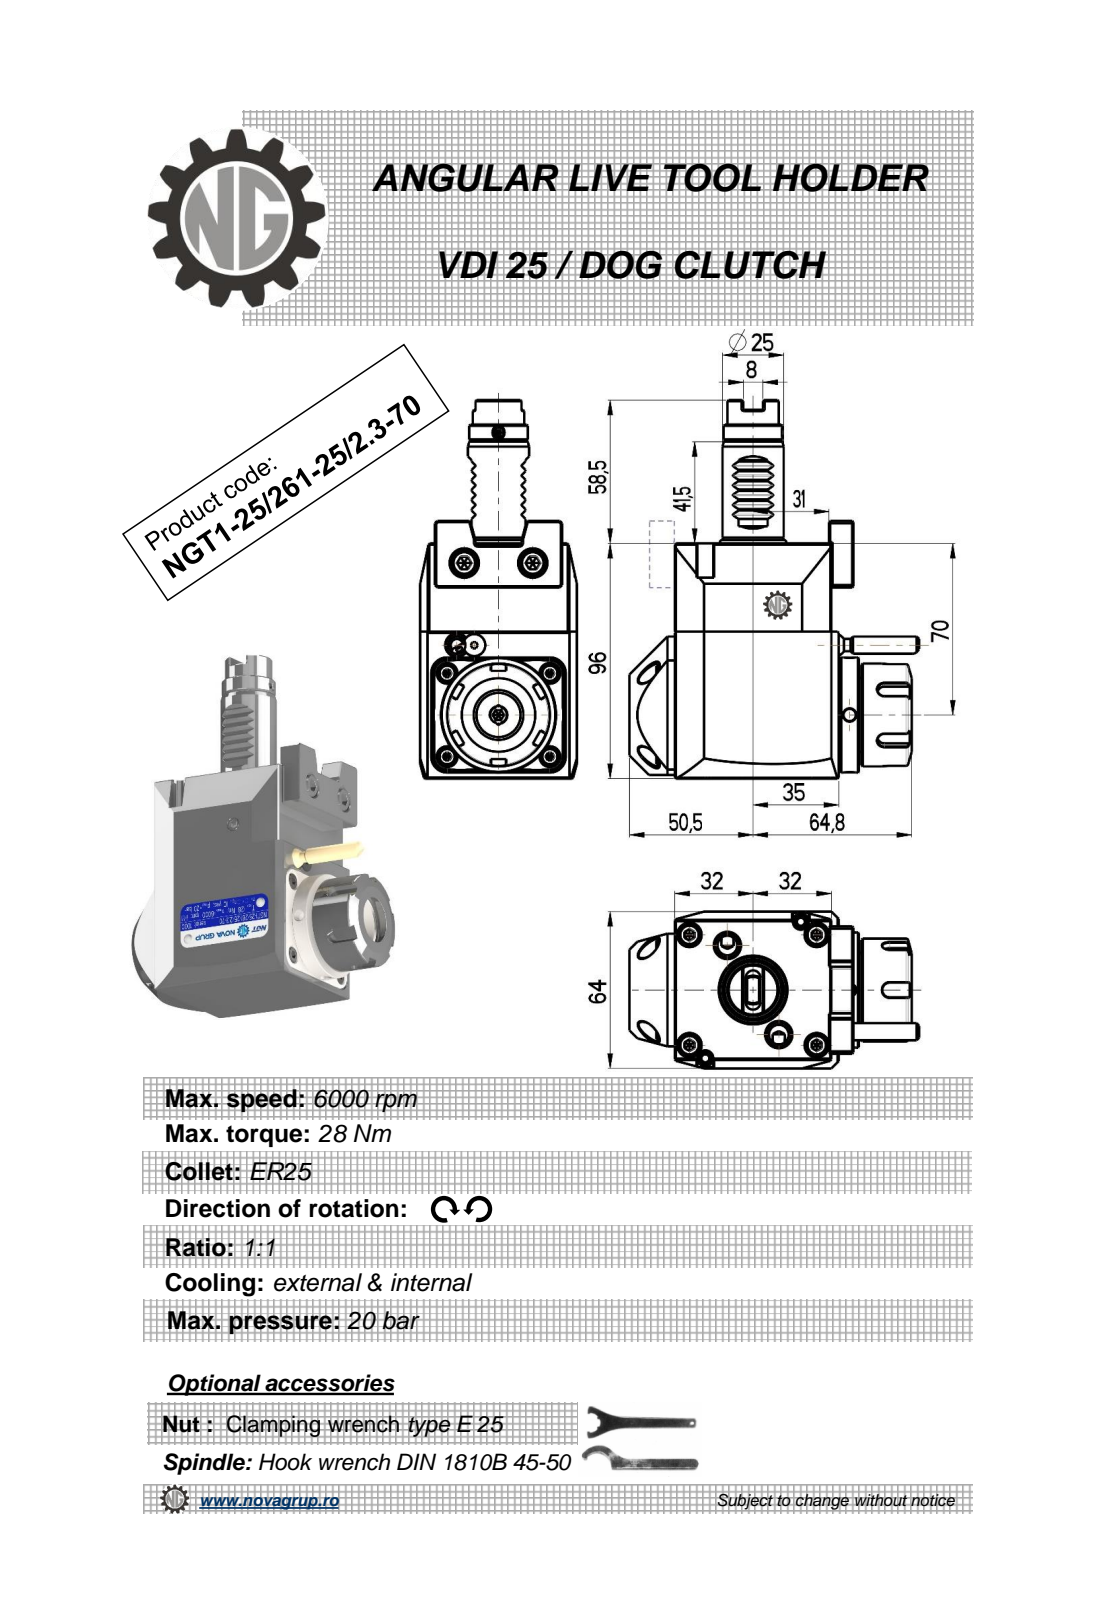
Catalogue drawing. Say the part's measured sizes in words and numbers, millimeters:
The part is named "NGT1_25_261_25_2_3_70". Its 3-D file was written by "PRO/ENGINEER BY PARAMETRIC TECHNOLOGY CORPORATION, 2010280 (CONFIG_CONTROL_DESIGN)". It is 1 solid with 418 faces: 214 planar, 66 cylindrical and 138 other. Overall it measures 154.5 by 118.33 by 64 millimeters. Its volume is 505 431 cubic millimeters and its surface area 49 640 square millimeters. Round holes: 2 of diameter 5, 1 of diameter 2.5, 1 of diameter 3, 1 of diameter 20.3. Round bosses or shafts: 1 of diameter 47, 1 of diameter 42, 1 of diameter 35, 1 of diameter 33, 1 of diameter 25, 1 of diameter 24, 1 of diameter 21, 1 of diameter 18.85. Partial cylindrical surfaces (rounded edges, fillets, slot ends): 12 of radius 0.3, 6 of radius 0.26, 5 of radius 3, 2 of radius 0.5, 2 of radius 1, 1 of radius 32. The main face-to-face distances are 64, 96, 6, 9, 67.2, 3, 3.2, 73, 5.8, 8. The hole center spacings are 33.19.
